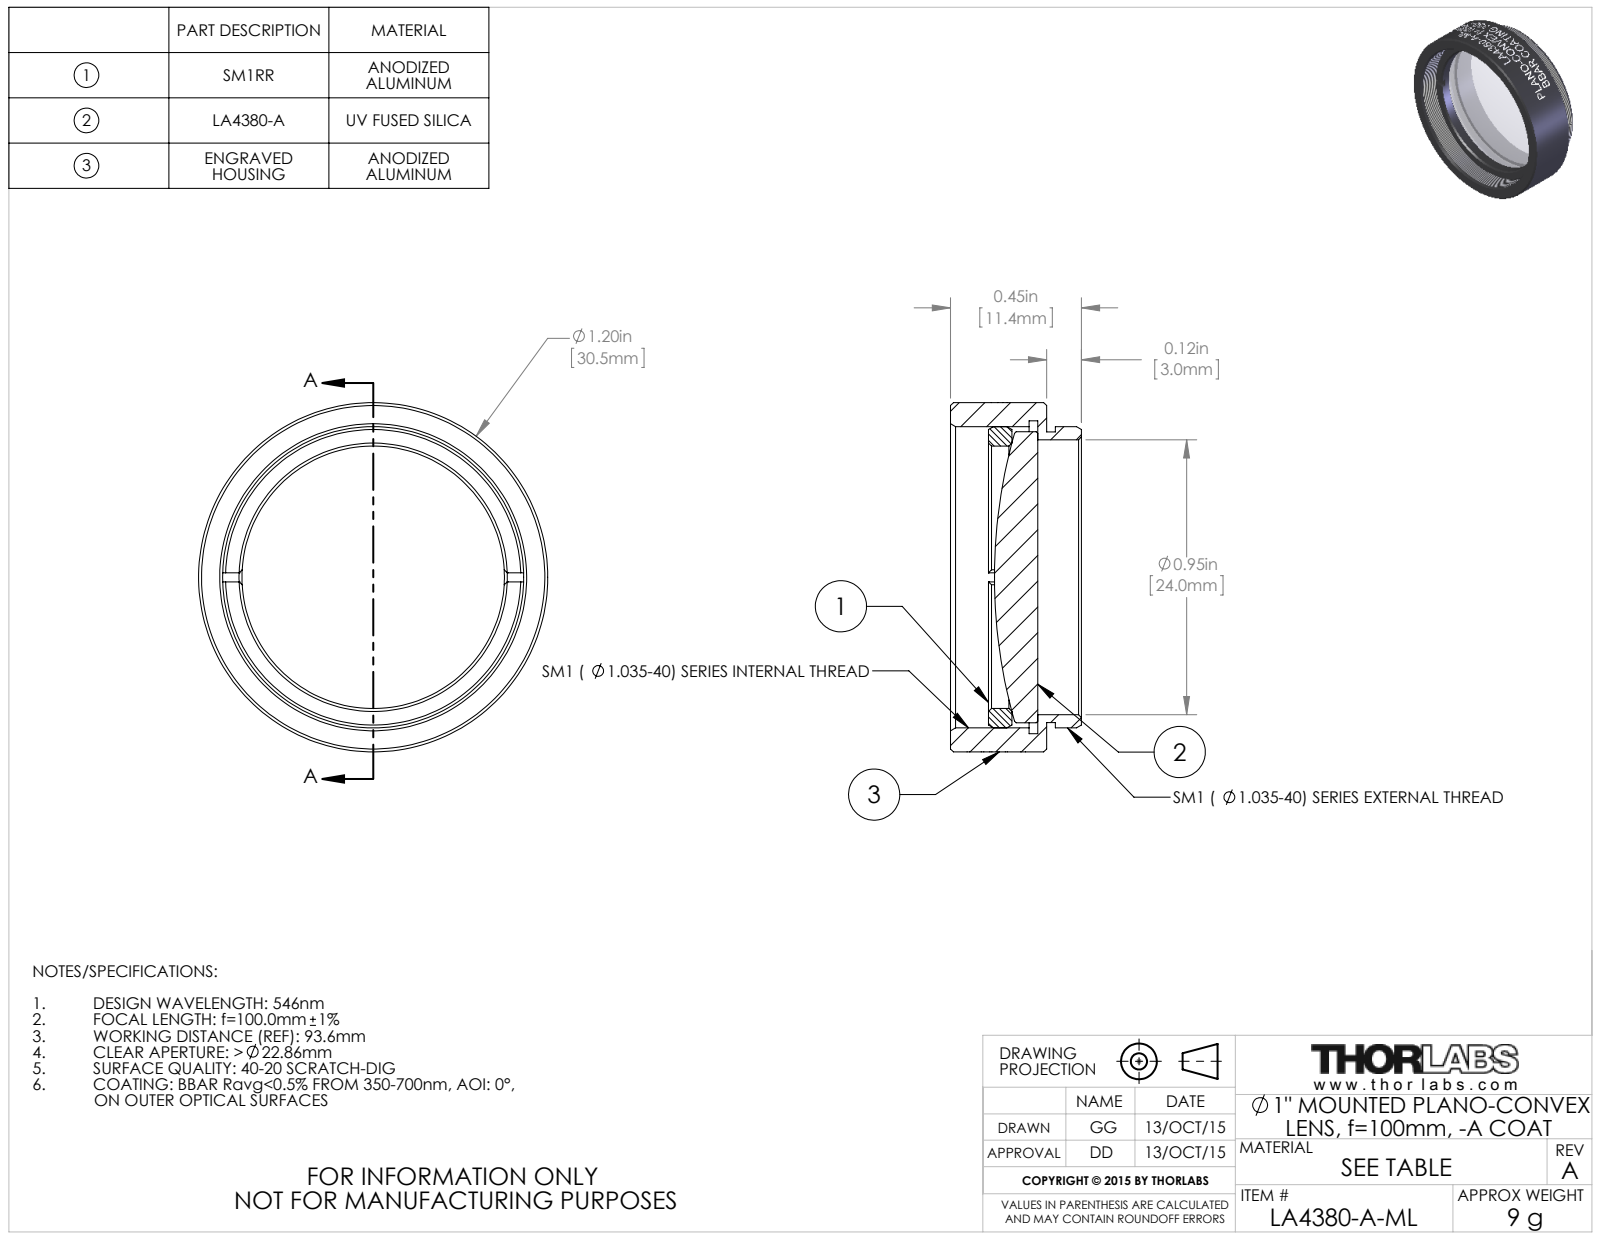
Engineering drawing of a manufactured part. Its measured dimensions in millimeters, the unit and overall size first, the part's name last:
Units: millimetres
Overall size (bounding box): 30.48 × 30.48 × 11.43
Round holes (diameter × count): ⌀22.91 ×1, ⌀24 ×1, ⌀27.31 ×1
Round bosses / shafts (diameter × count): ⌀30.48 ×1, ⌀26.29 ×1, ⌀25.4 ×1, ⌀25.37 ×1
Main face-to-face distances: 0.76, 8.38, 7.62, 3.04, 2.28, 5.34, 5.07, 4.31, 2.03, 3.31
Volume: 3 550 mm³ · Surface area: 4 312 mm²
Bodies: 3 solids, 162 faces (20 planar, 114 cylindrical, 28 other)
Part name (STEP PRODUCT): TTN039261-E0W
STEP written by: SolidWorks 2014 (CONFIG_CONTROL_DESIGN)
